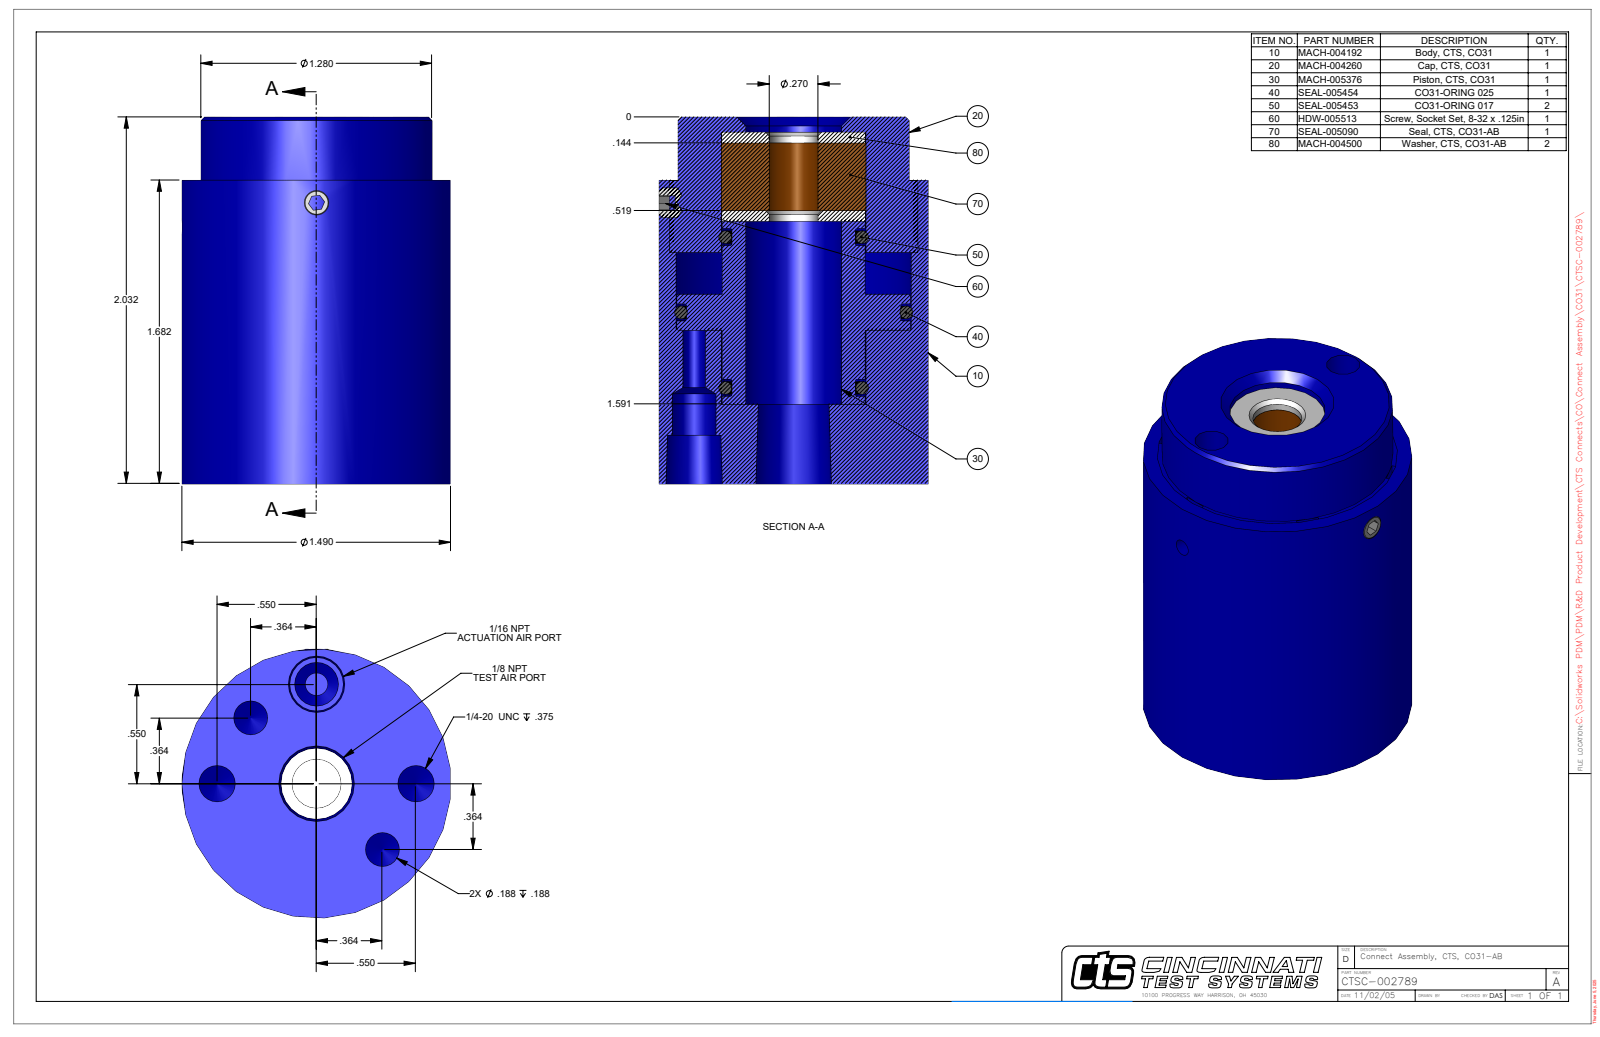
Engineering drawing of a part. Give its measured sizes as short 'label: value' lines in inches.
name: CTSC-002789
written by: SolidWorks 2023 (AUTOMOTIVE_DESIGN)
unit: in
bodies: 1 solid, 111 faces (53 planar, 40 cylindrical, 18 other)
size: 2.032 × 1.49 × 1.49
volume: 2.991 in³; area: 17.03 in²
holes: 4× ⌀0.187, 2× ⌀0.201, 1× ⌀0.094, 1× ⌀0.136, 1× ⌀0.242, 1× ⌀0.27, 1× ⌀0.272, 1× ⌀0.53, 1× ⌀0.8, 1× ⌀1.33
bosses: 1× ⌀1.49, 1× ⌀1.28, 1× ⌀0.792
rounds: 1× R0.687, 1× R0.735
face distances: 2.032, 1.682, 0.35, 1.454, 0.228, 0.578, 1.947, 0.493, 0.265, 0.085
hole spacings: 0.515, 0.409, 0.55, 0.984, 0.035, 0.394, 0.754, 0.778
